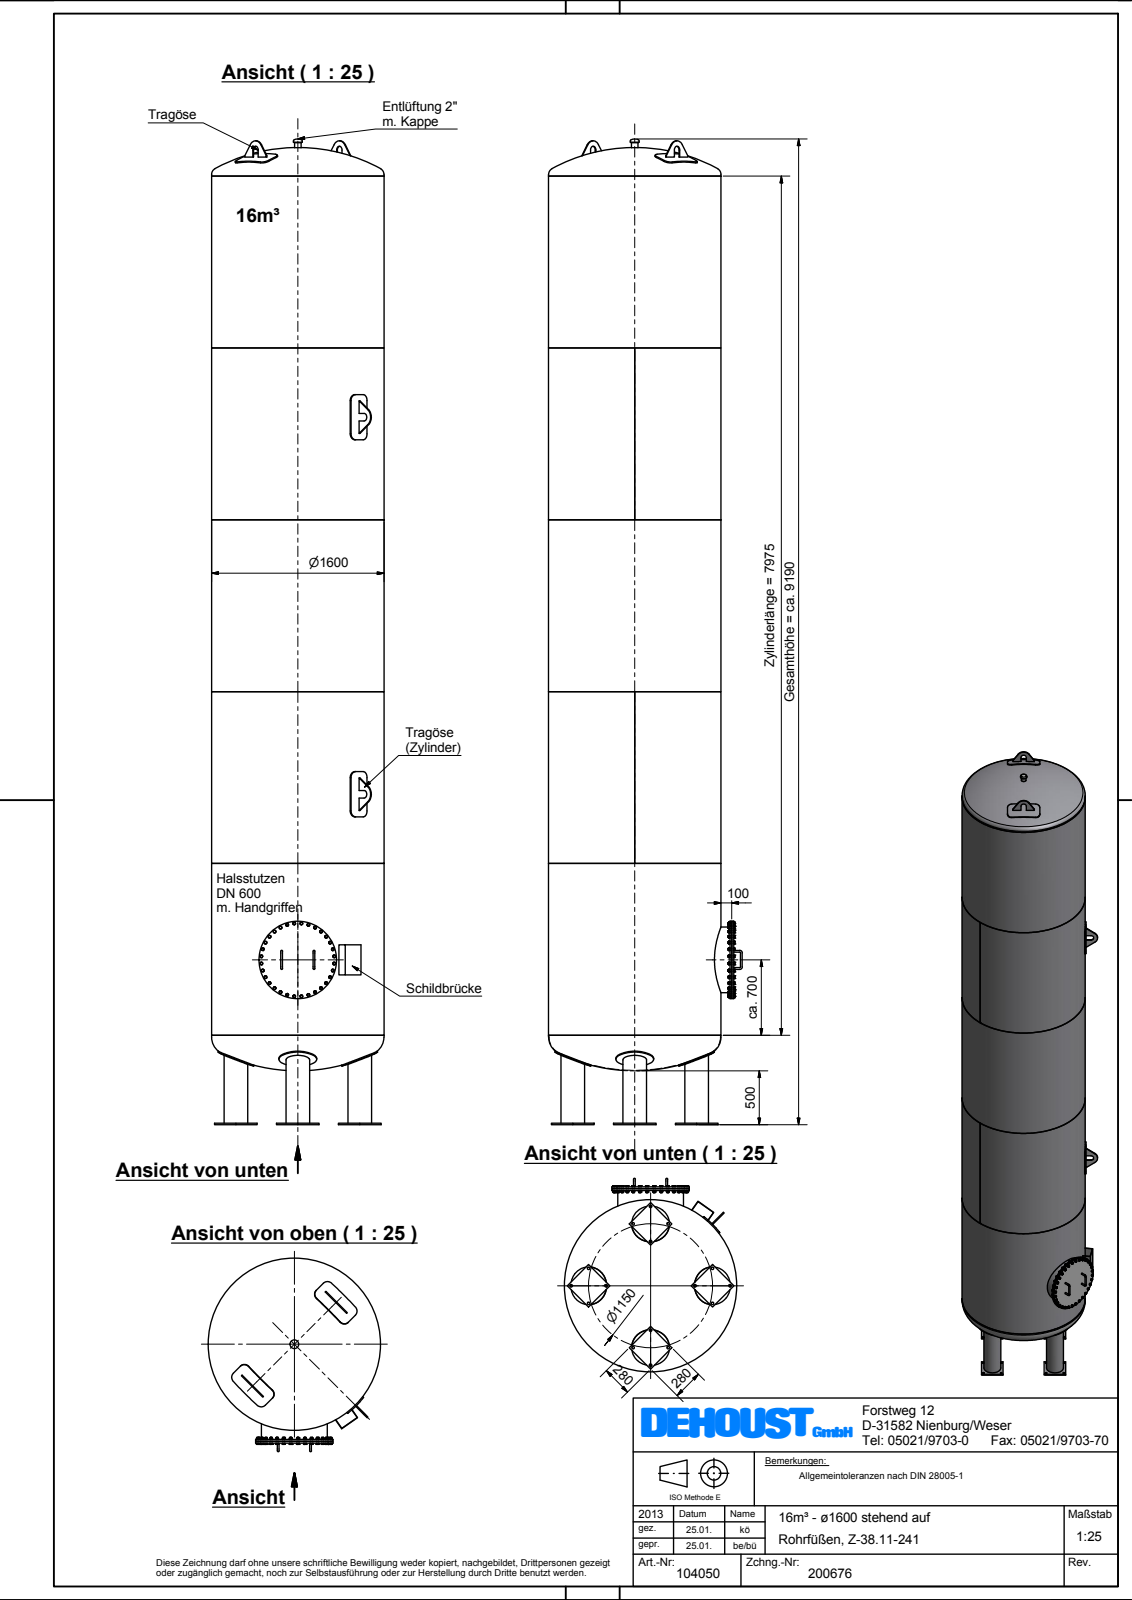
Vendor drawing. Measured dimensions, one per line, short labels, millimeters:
name: Beh\S\dlter_Z-38_11-241_1600_016_KV
written by: Autodesk Inventor 2012 (AUTOMOTIVE_DESIGN)
unit: mm
bodies: 7 solids, 1122 faces (636 planar, 164 cylindrical, 322 other)
size: 9151.04 × 1797 × 1600
volume: 698 800 000 mm³; area: 96 100 000 mm²
holes: 4× ⌀203.1, 1× ⌀598, 1× ⌀1590
bosses: 38× ⌀16, 32× ⌀22.5, 4× ⌀350, 4× ⌀219.1, 1× ⌀1600, 1× ⌀720, 1× ⌀660, 1× ⌀610
rounds: 16× R56, 4× R35, 4× R85, 1× R810
face distances: 35, 830.57, 15, 815.57, 16, 19, 10, 3, 2.93, 549.42
hole spacings: 575, 813.17, 1150
